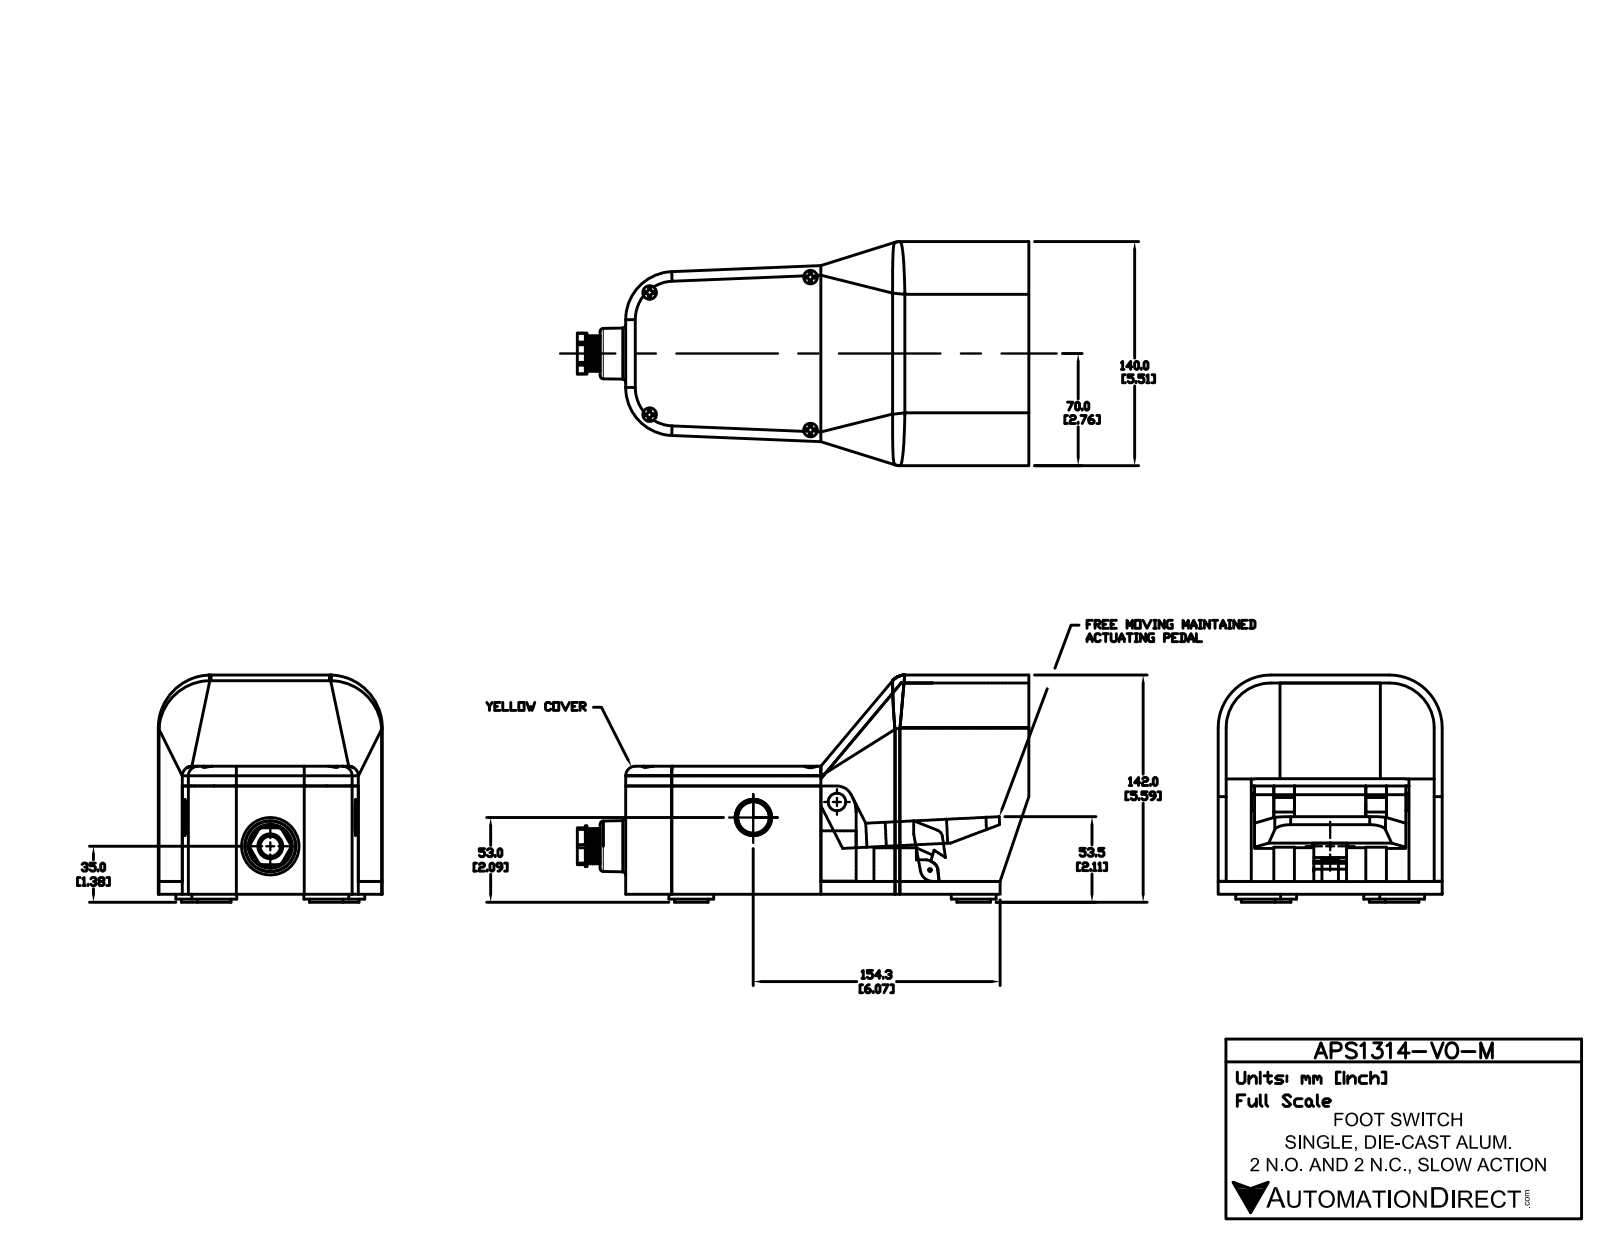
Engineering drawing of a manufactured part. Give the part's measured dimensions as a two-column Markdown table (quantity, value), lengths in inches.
| quantity | value |
| --- | --- |
| part name | APS1314-V0-M |
| STEP written by | SolidWorks 2015 (AUTOMOTIVE_DESIGN) |
| units | inches |
| bodies | 19 solids, 400 faces (242 planar, 102 cylindrical, 56 other) |
| overall size | 11.112 × 5.591 × 5.512 |
| volume | 94.89 in³ |
| surface area | 423.5 in² |
| round holes (diameter × count) | 0.335 × 4, 0.896 × 2, 0.498 × 1, 0.614 × 1 |
| round bosses / shafts (diameter × count) | 1.102 × 4, 0.827 × 4, 0.782 × 2, 1.004 × 1, 0.866 × 1, 0.433 × 1, 0.075 × 1 |
| partial cylindrical surfaces (radius × count) | 0.039 × 16, 0.394 × 6, 0.197 × 4, 0.236 × 3, 1.102 × 2, 1.181 × 2, 1.299 × 2, 0.315 × 1 |
| main face-to-face distances | 0.197, 5.315, 0.315, 2.348, 2.664, 2.349, 2.663, 5.512, 2.835, 3.15 |
| hole center spacings | 3.976, 5.206, 3.004, 3.76 |
